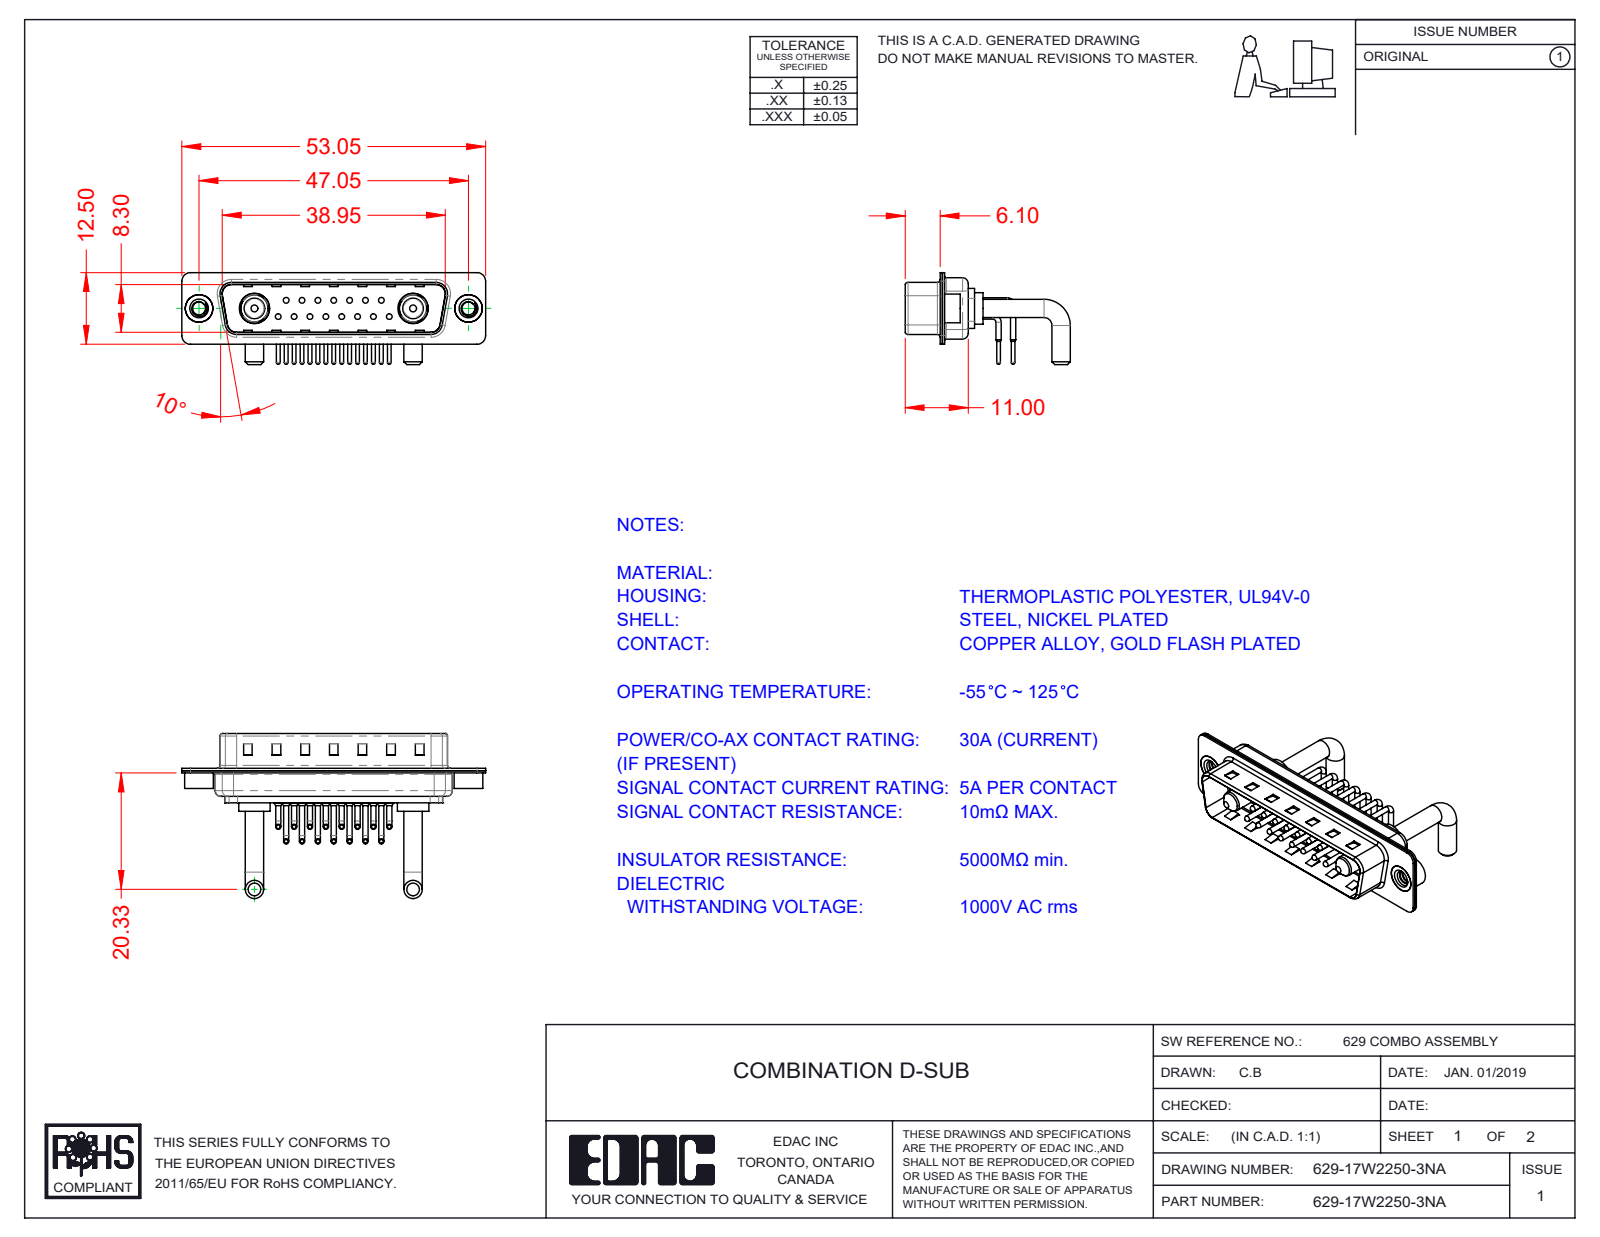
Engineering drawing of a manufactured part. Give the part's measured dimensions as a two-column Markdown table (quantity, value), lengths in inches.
| quantity | value |
| --- | --- |
| part name | 629Combo Contact Row 2; 629Combo Threaded Rivet_2; 629Combo Shell Front_25 Contacts; 629Combo Housing_17W2 (+4 more) |
| STEP written by | SolidWorks 2020 (CONFIG_CONTROL_DESIGN) |
| units | inches |
| bodies | 24 solids, 2112 faces (1151 planar, 719 cylindrical, 242 other) |
| overall size | 2.089 × 1.135 × 0.632 |
| volume | 0.2 in³ |
| surface area | 11.87 in² |
| round holes (diameter × count) | 0.03 × 15, 0.063 × 15, 0.079 × 15, 0.089 × 2, 0.157 × 2, 0.189 × 2, 0.191 × 2, 0.209 × 2 |
| round bosses / shafts (diameter × count) | 0.035 × 30, 0.059 × 15, 0.039 × 15, 0.026 × 15, 0.126 × 4, 0.217 × 2, 0.205 × 2, 0.197 × 2 |
| partial cylindrical surfaces (radius × count) | 0.059 × 16, 0.04 × 15, 0.079 × 12, 0.02 × 8, 0.063 × 8, 0.01 × 4, 0.024 × 4, 0.026 × 4 |
| main face-to-face distances | 0.016, 0.031, 0.374, 0.358, 0.343, 0.39, 0.03, 0.22, 0.047, 0.014 |
| hole center spacings | 0.124, 0.109, 0.218, 0.327, 0.198, 0.295, 0.436, 0.198 |
